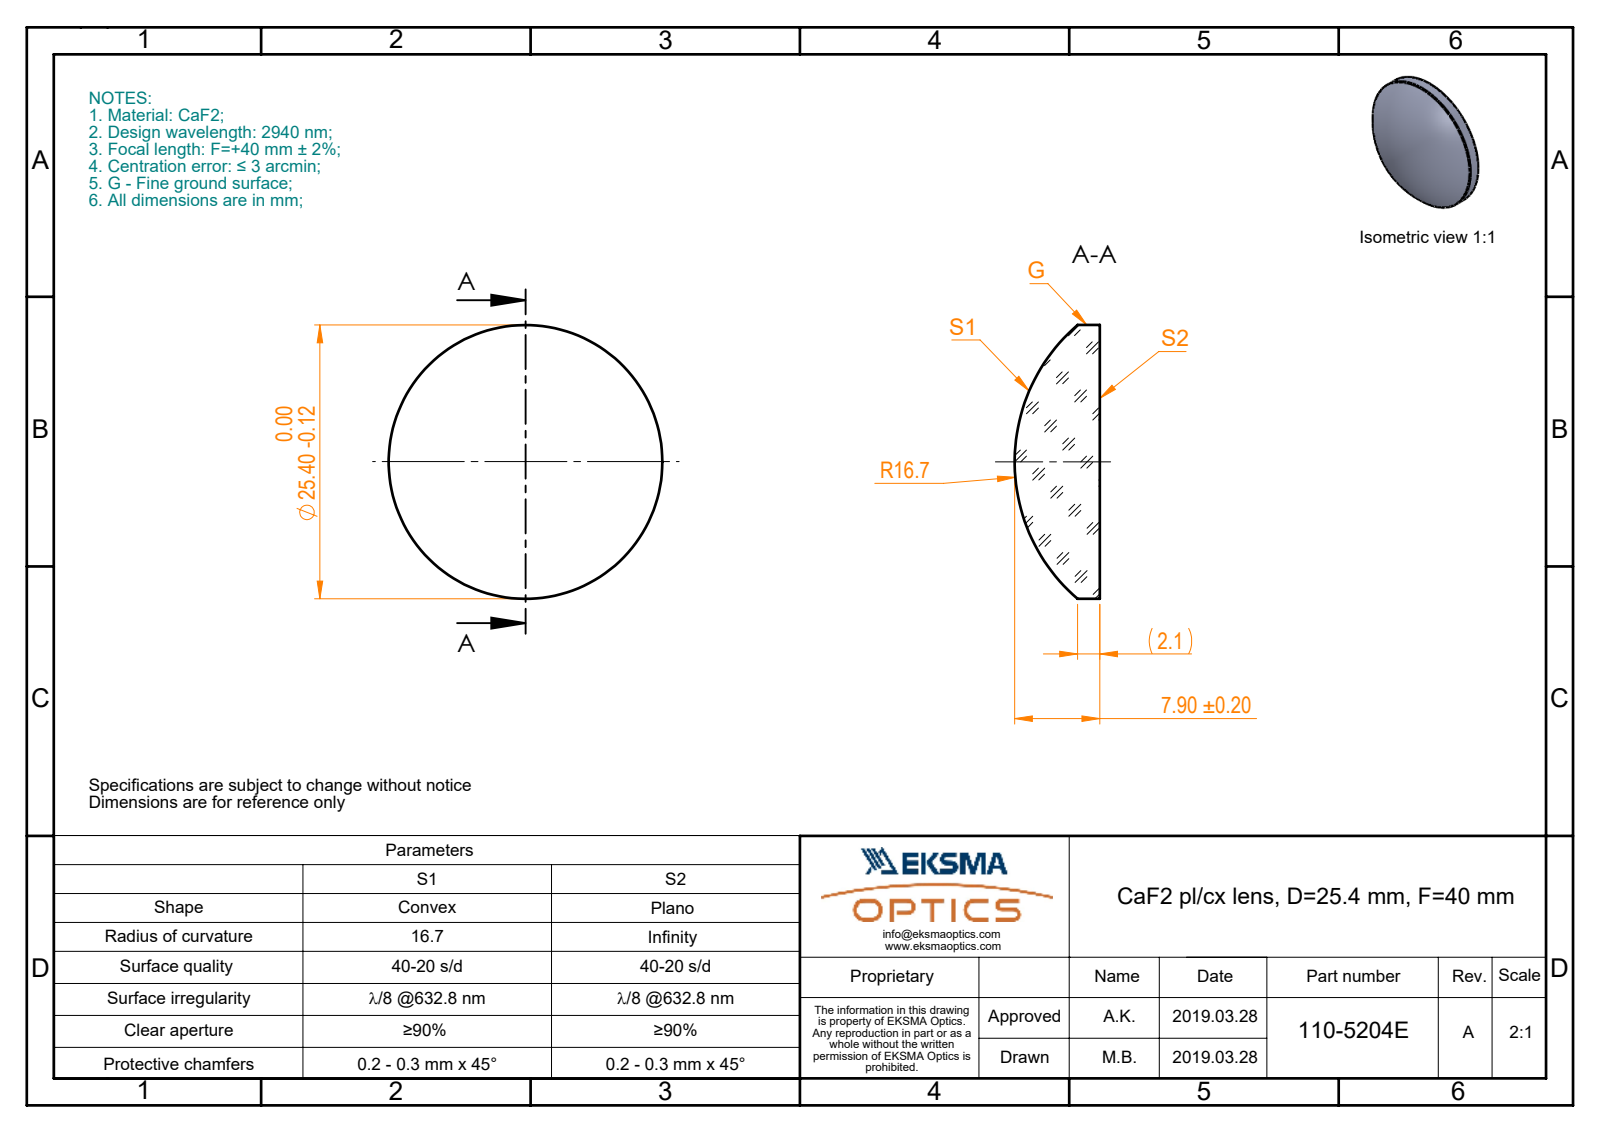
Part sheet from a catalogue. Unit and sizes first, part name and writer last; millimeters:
Units: millimetres
Overall size (bounding box): 25.4 × 25.4 × 7.9
Round bosses / shafts (diameter × count): ⌀25.4 ×1
Volume: 2 628 mm³ · Surface area: 1 285 mm²
Bodies: 1 solid, 5 faces (1 planar, 2 cylindrical, 2 other)
Part name (STEP PRODUCT): 110-5204E CaF2 pl-cx 25.4 F40
STEP written by: SolidWorks 2017 (CONFIG_CONTROL_DESIGN)
